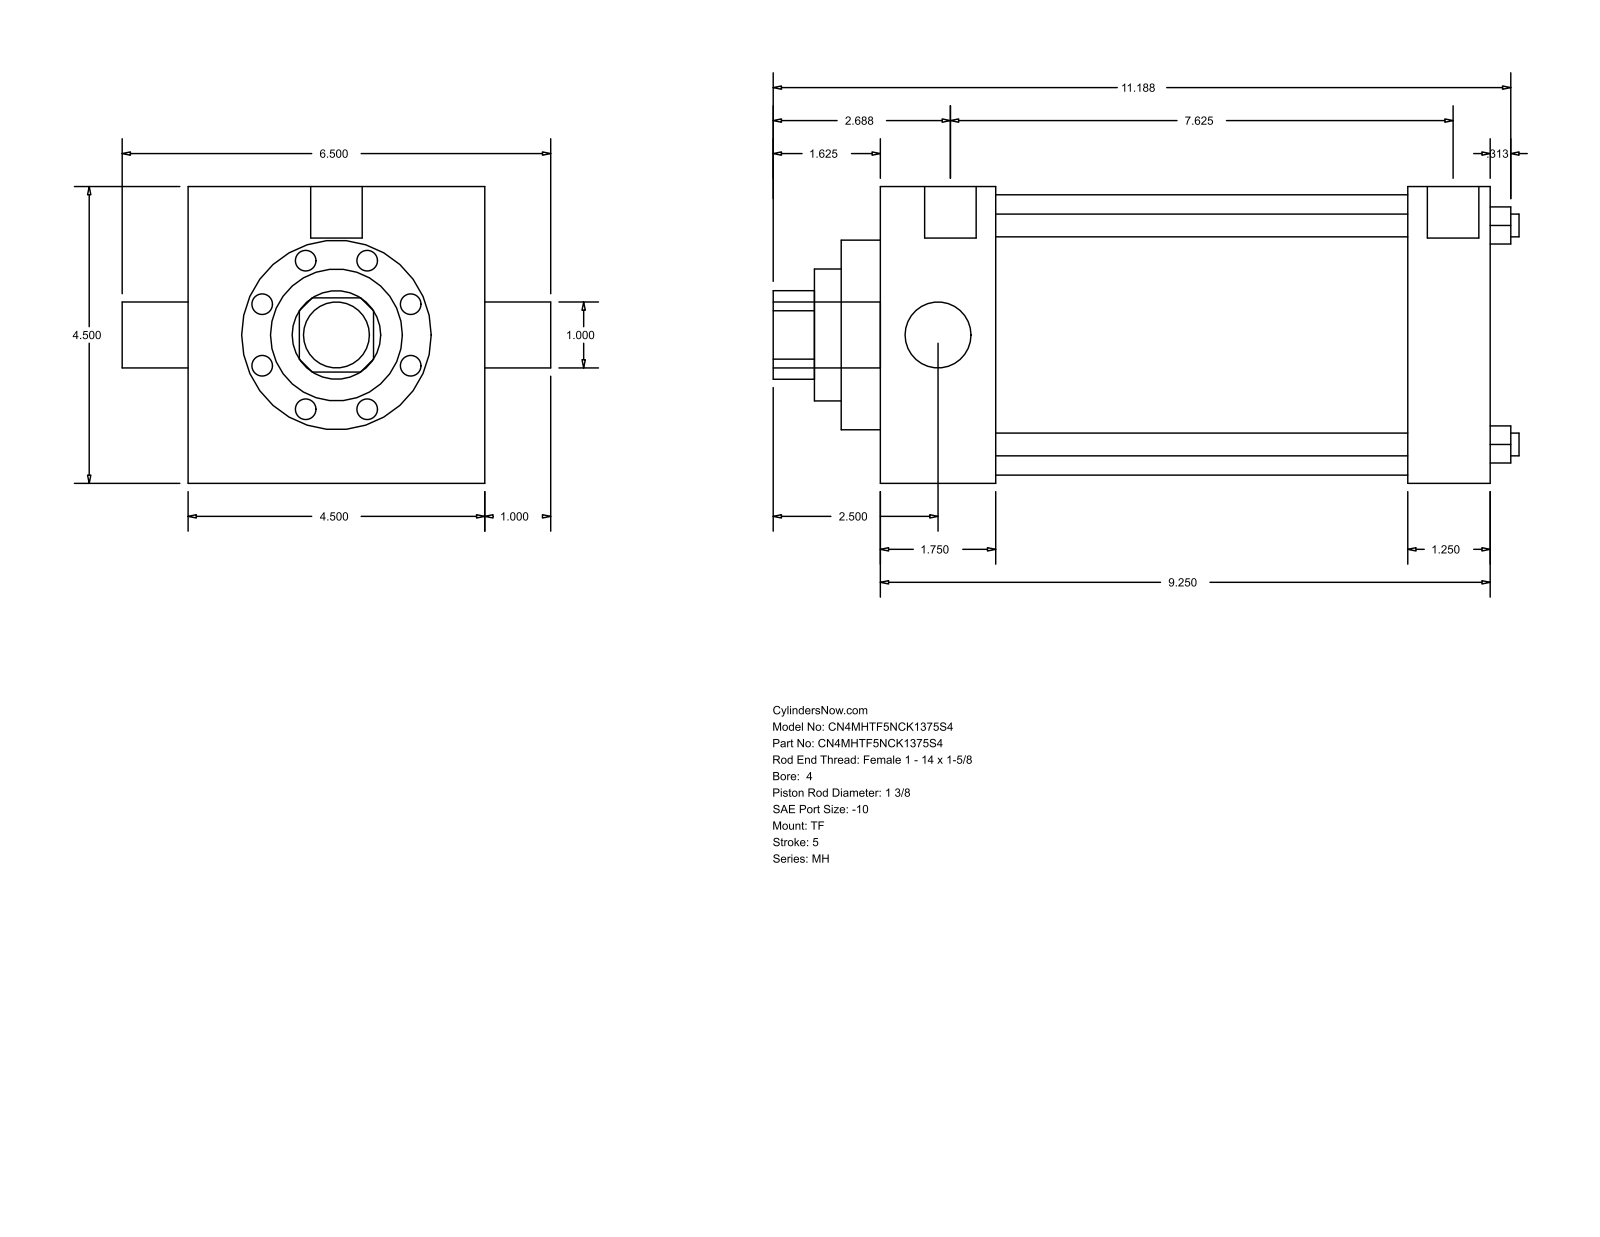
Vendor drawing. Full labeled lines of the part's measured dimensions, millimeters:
Part name (STEP PRODUCT): MH_TF__0400_1.375
STEP written by: GSSL Pune (CONFIG_CONTROL_DESIGN)
Units: millimetres
Bodies: 0 solids, 86 faces (61 planar, 25 cylindrical, 0 other)
Overall size (bounding box): 287.34 × 165.1 × 114.3
Round holes (diameter × count): ⌀8.76 ×4, ⌀25.4 ×1, ⌀34.92 ×1, ⌀50.8 ×1, ⌀73.03 ×1, ⌀107.95 ×1
Round bosses / shafts (diameter × count): ⌀8.73 ×3, ⌀19.84 ×2, ⌀25.4 ×1
Partial cylindrical surfaces — rounded edges, fillets, slot ends (radius × count): R17.06 ×1
Main face-to-face distances: 114.3, 234.96, 44.45, 190.51, 203.2, 158.75, 31.76, 15.08, 59.53, 218.28
Hole centre spacings: 59.62, 84.32, 119.25
